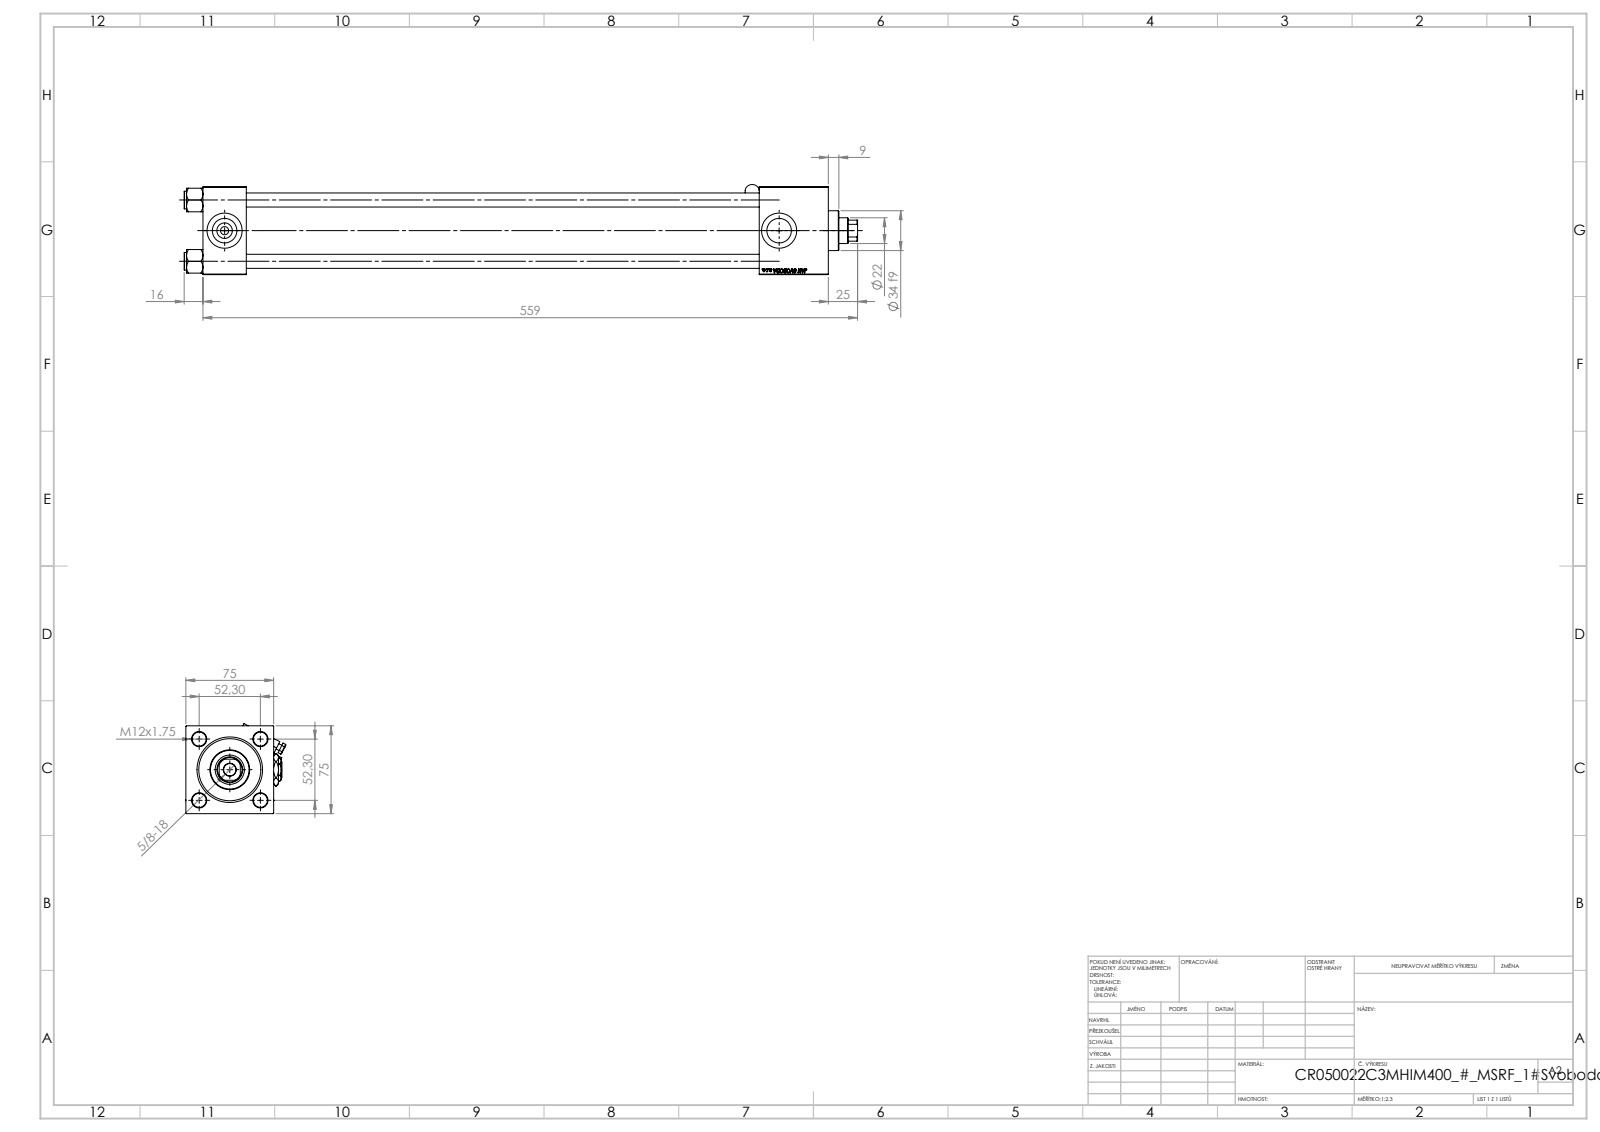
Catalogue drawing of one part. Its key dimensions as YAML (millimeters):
part_name: "NUT_M5_C; V215CR_C_Body; V215_VC_A; V215CR_VCP_C (+3 more)"
step_written_by: "SolidWorks 2019 (CONFIG_CONTROL_DESIGN)"
units: millimeters
bodies: {solids: 14, faces: 1281, planar: 591, cylindrical: 112, other: 578}
overall_size: [575, 85.68, 76.88]
volume: 1162000
surface_area: 364119
round_holes:
  - {diameter: 12, count: 4}
  - {diameter: 7, count: 2}
  - {diameter: 20.96, count: 2}
  - {diameter: 30, count: 2}
  - {diameter: 10.5, count: 1}
  - {diameter: 22, count: 1}
  - {diameter: 25, count: 1}
  - {diameter: 41, count: 1}
  - {diameter: 50, count: 1}
  - {diameter: 53, count: 1}
round_bosses_or_shafts:
  - {diameter: 15, count: 4}
  - {diameter: 56, count: 1}
  - {diameter: 34, count: 1}
  - {diameter: 5, count: 1}
  - {diameter: 2.5, count: 1}
partial_cylinders:
  - {radius: 0.5, count: 6}
  - {radius: 6, count: 2}
  - {radius: 10.5, count: 1}
face_to_face_distances: [75, 37, 534, 497, 475, 438, 59, 505.3, 468.3, 30.3]
hole_center_spacings: [36.98, 52.3, 73.96, 473.5]
